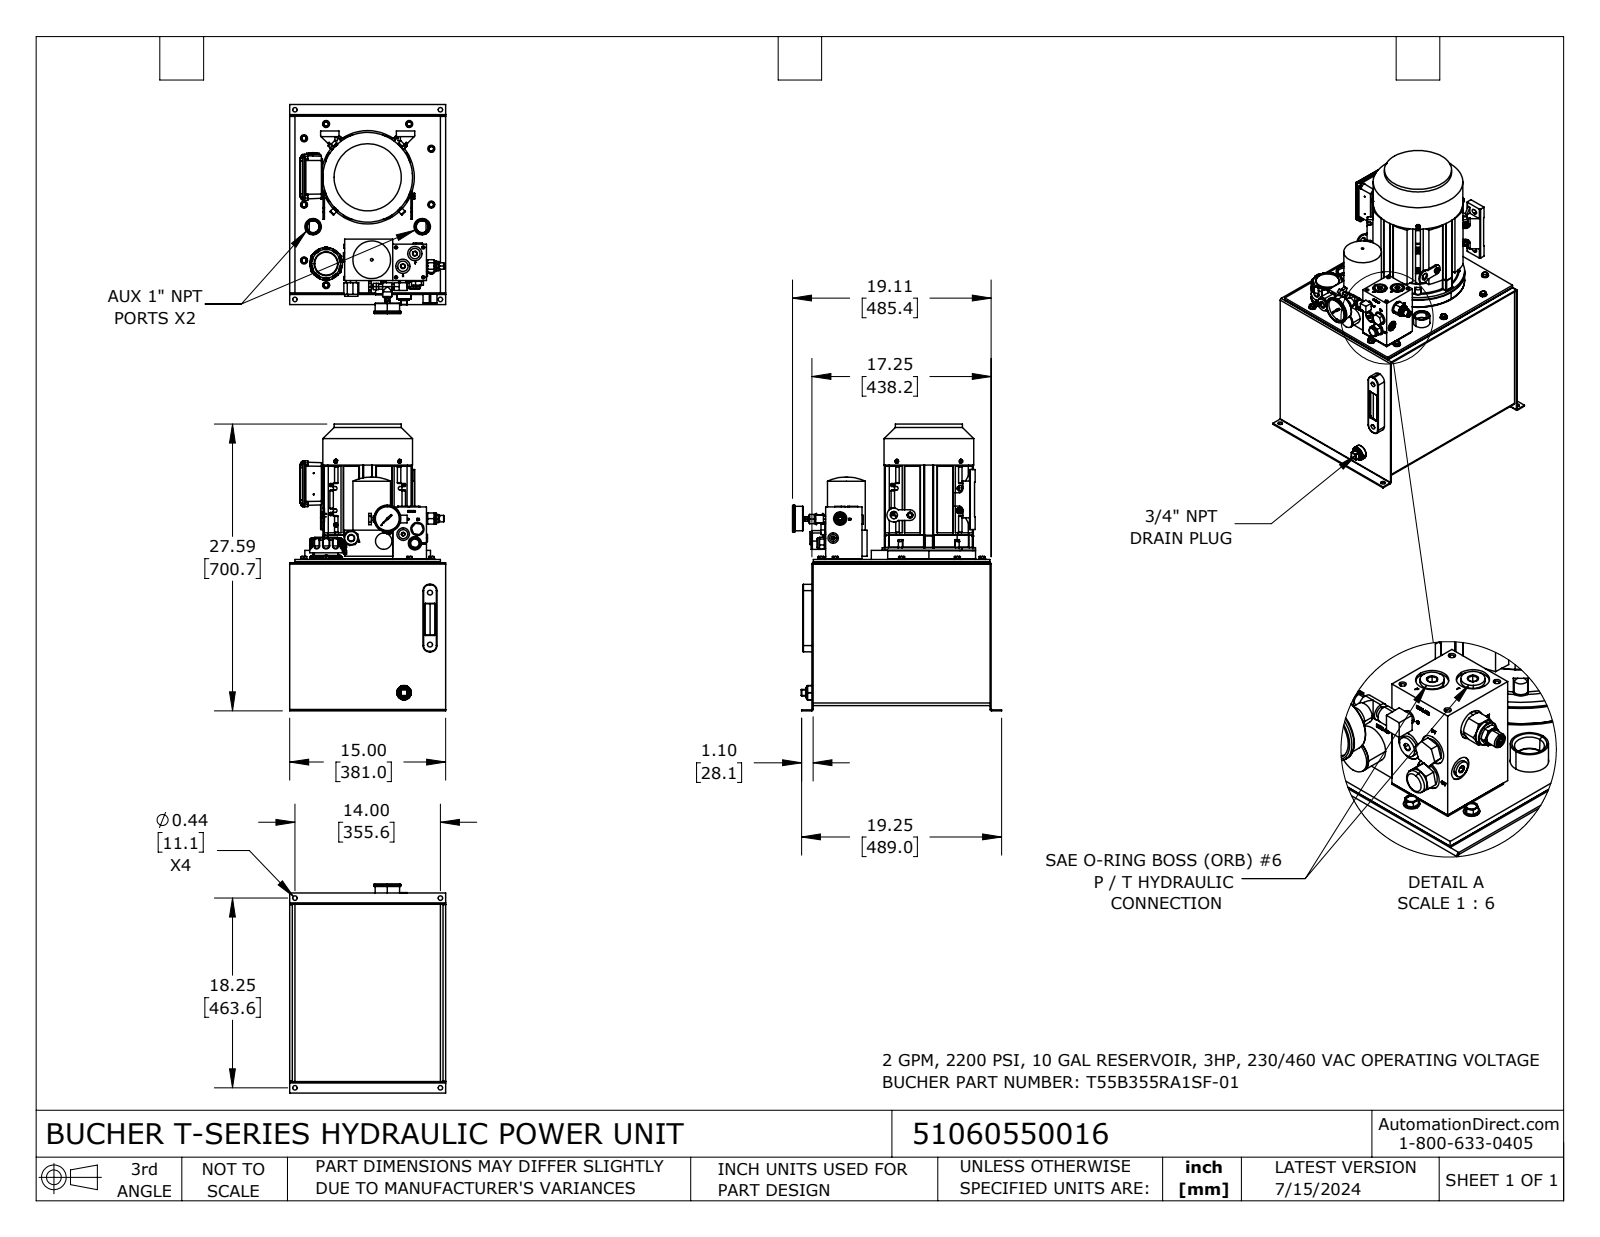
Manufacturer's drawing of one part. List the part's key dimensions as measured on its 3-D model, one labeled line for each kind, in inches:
Part name (STEP PRODUCT): 51060550016
STEP written by: SolidWorks 2023 (CONFIG_CONTROL_DESIGN)
Units: inches
Bodies: 118 solids, 4726 faces (2314 planar, 1525 cylindrical, 887 other)
Overall size (bounding box): 27.585 × 20.112 × 15
Volume: 1 108 in³ · Surface area: 5 010 in²
Round holes (diameter × count): ⌀0.437 ×17, ⌀0.236 ×15, ⌀0.5 ×11, ⌀0.197 ×10, ⌀0.563 ×10, ⌀0.201 ×8, ⌀0.19 ×6, ⌀0.315 ×6, ⌀0.472 ×6, ⌀0.531 ×6, ⌀0.807 ×5, ⌀1.37 ×5
Round bosses / shafts (diameter × count): ⌀0.676 ×10, ⌀0.313 ×10, ⌀0.394 ×7, ⌀0.551 ×6, ⌀0.472 ×6, ⌀0.373 ×6, ⌀0.25 ×5, ⌀0.37 ×4
Partial cylindrical surfaces — rounded edges, fillets, slot ends (radius × count): R0.02 ×188, R0.079 ×96, R0.039 ×52, R0.063 ×21, R0.375 ×15, R0.05 ×13, R0.04 ×12, R0.125 ×12
Main face-to-face distances: 0.104, 0.105, 14.395, 17.145, 0.25, 0.313, 13.635, 0.063, 13.802, 14.5
Hole centre spacings: 2.15, 3.469, 6.6, 7.024, 2.927, 3.976, 5.27, 0.78
